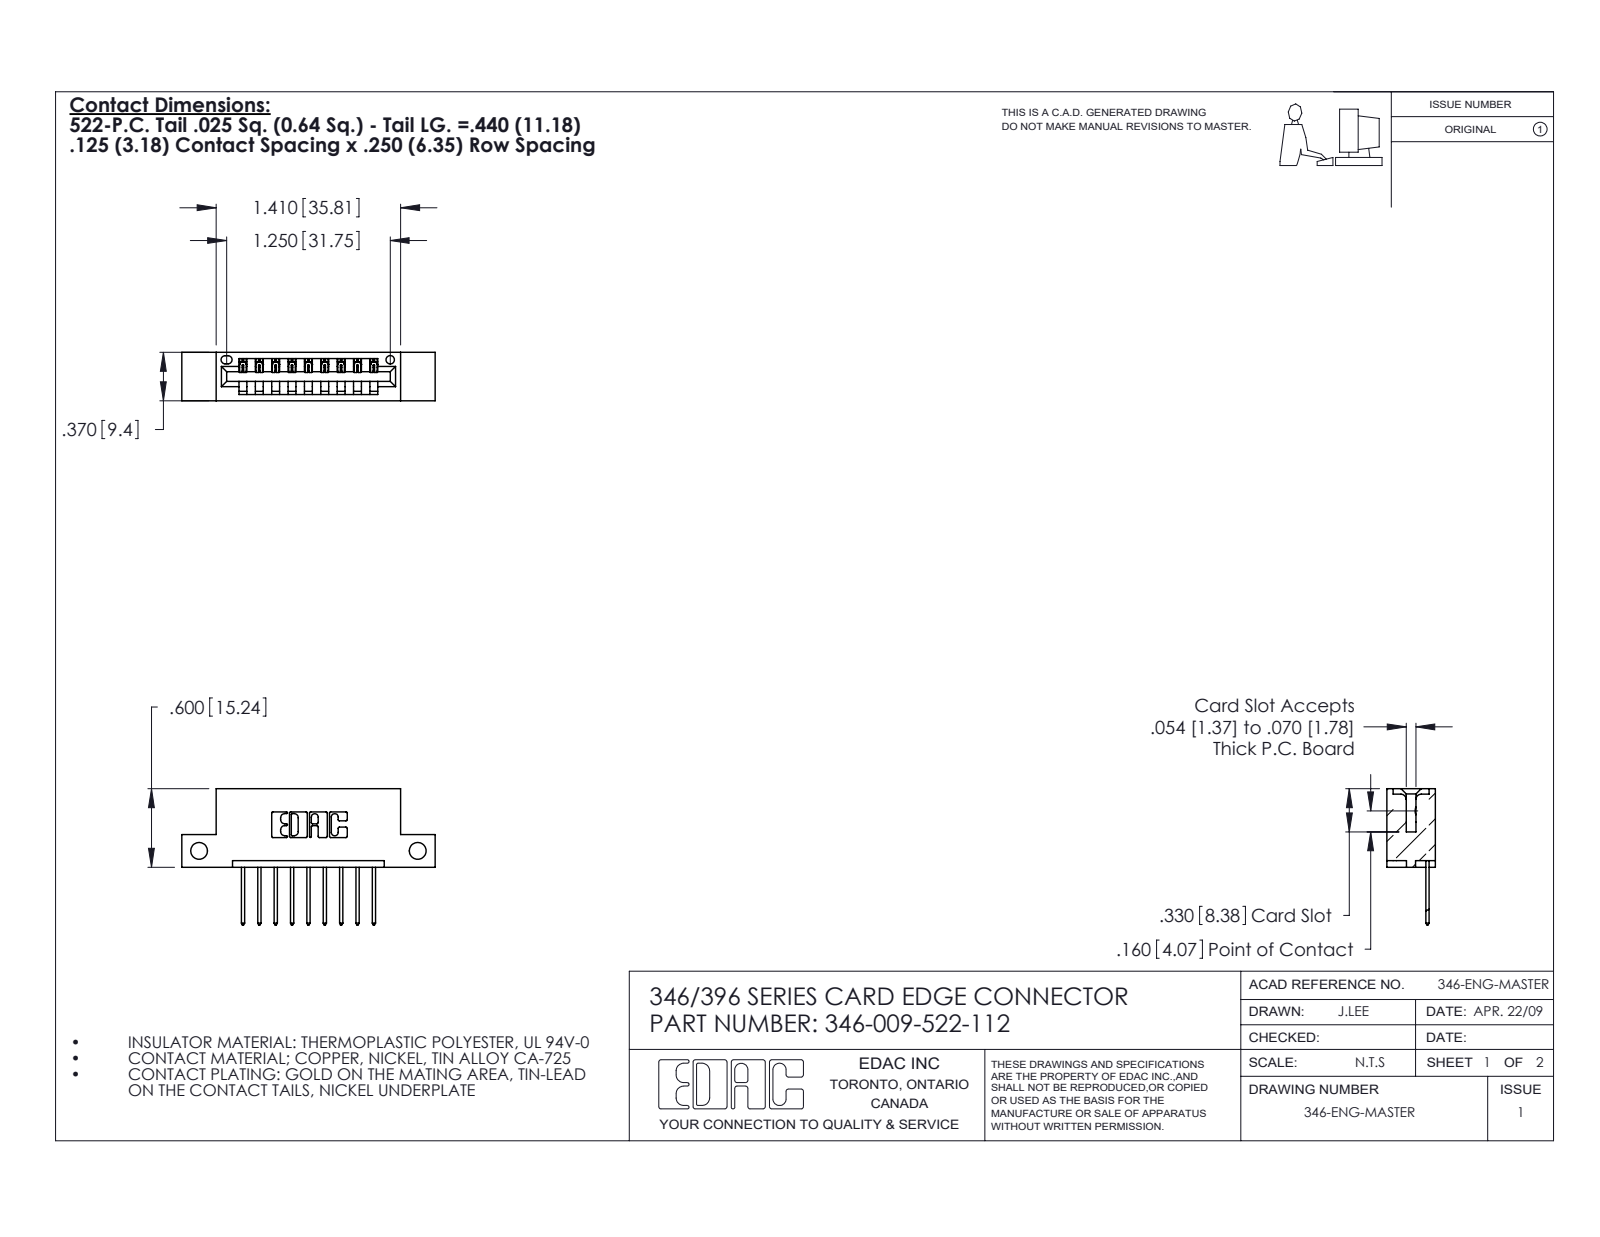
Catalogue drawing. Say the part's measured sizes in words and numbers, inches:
The part is named "345-292-001_345-293-122; 346 Part_Flush Mounting Lugs - Side Mount; 346-009-522-112". Its 3-D file was written by "SolidWorks 2020 (CONFIG_CONTROL_DESIGN)". It is 10 solids with 644 faces: 436 planar, 208 cylindrical and 0 other. Overall it measures 1.935 by 1.04 by 0.37 inches. Its volume is 0.268 cubic inches and its surface area 7.78 square inches. Round holes: 2 of diameter 0.128, 1 of diameter 0.064. Partial cylindrical surfaces (rounded edges, fillets, slot ends): 22 of radius 0.01, 18 of radius 0.006, 18 of radius 0.01, 6 of radius 0.007, 6 of radius 0.031, 3 of radius 0.026, 2 of radius 0.031, 2 of radius 0.04. The main face-to-face distances are 0.25, 0.048, 0.322, 0.37, 0.072, 0.298, 0.025, 0.148, 0.222, 0.1. The hole center spacings are 1.67.
